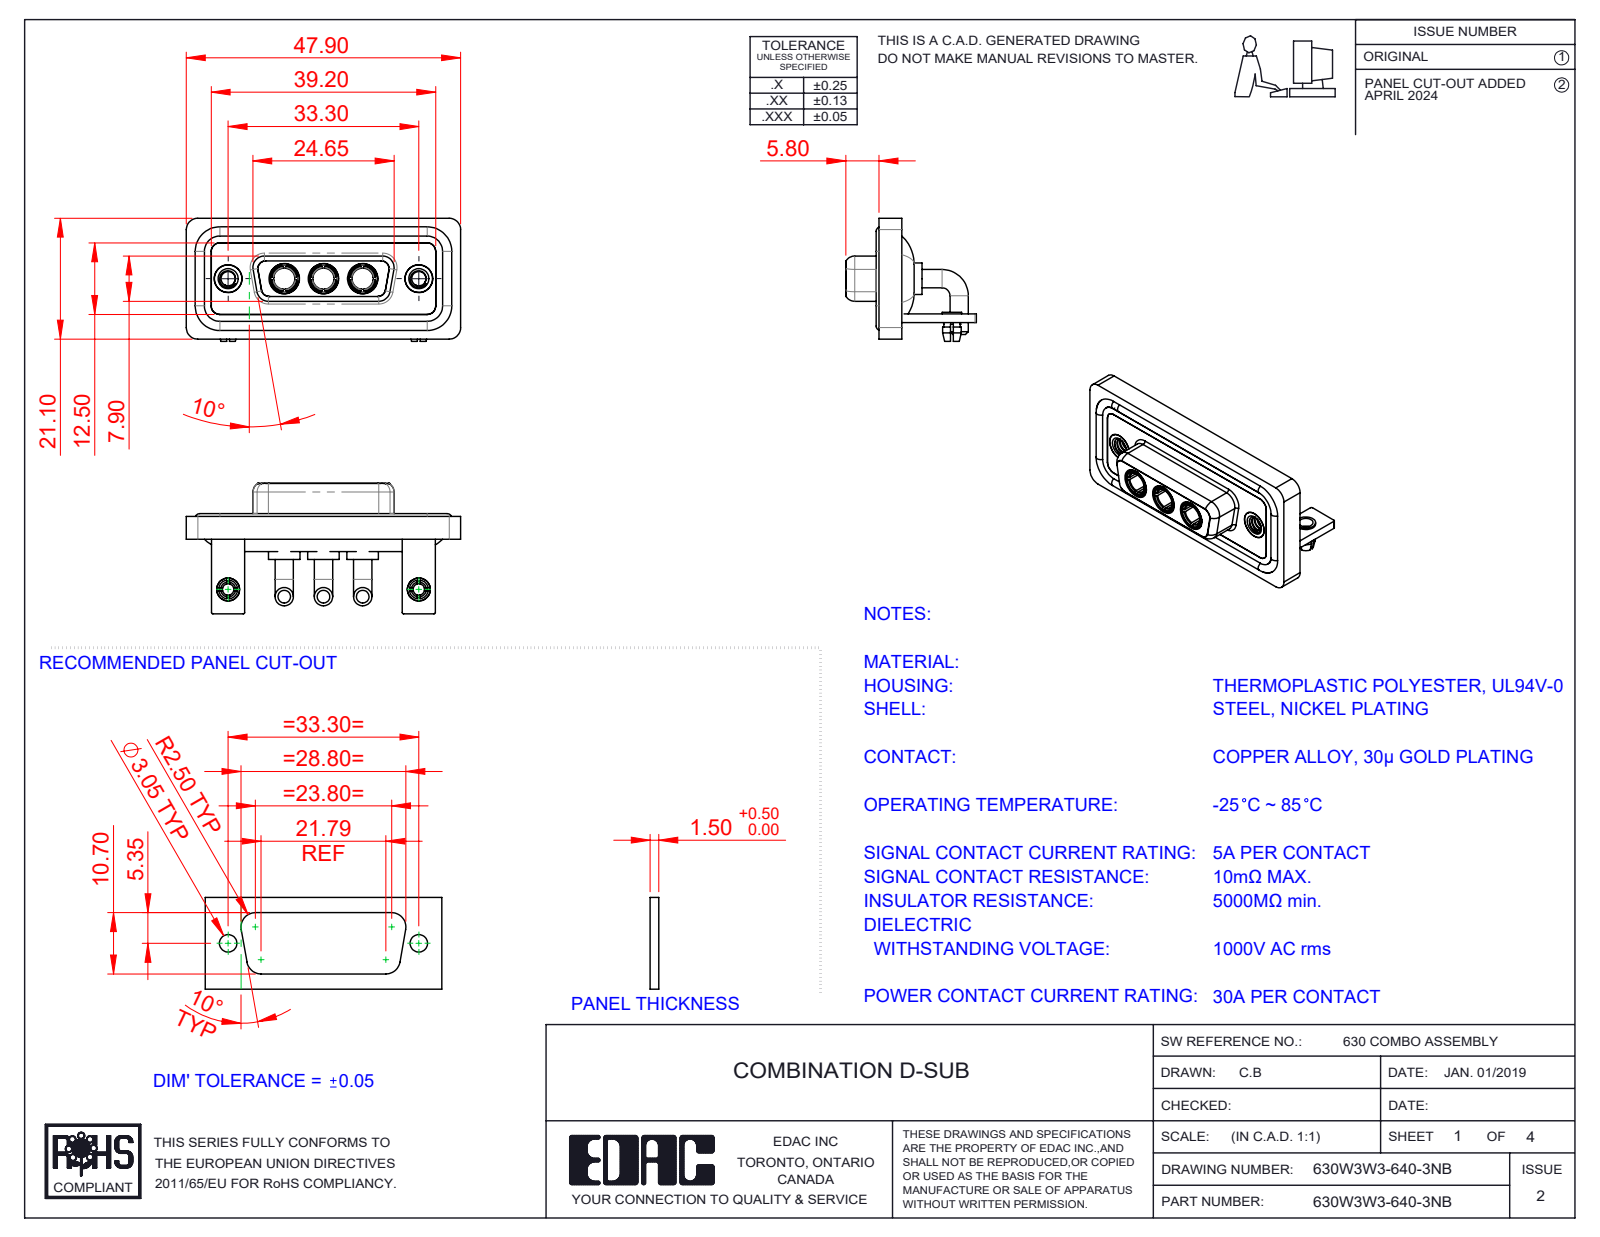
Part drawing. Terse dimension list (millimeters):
name: 630W3W3-640-3NB; 630Combo Shell Front_15 Contacts; 630Combo Housing_3W3; 630Combo Stabilizer Bracket_50 Contacts (+5 more)
written by: SolidWorks 2023 (CONFIG_CONTROL_DESIGN)
unit: mm
bodies: 17 solids, 754 faces (260 planar, 317 cylindrical, 177 other)
size: 47.9 × 22.8 × 21.5
volume: 6 659 mm³; area: 10 976 mm²
holes: 5× ⌀4.85, 4× ⌀2.5, 3× ⌀3.7, 3× ⌀5.3, 2× ⌀2, 2× ⌀3.2, 2× ⌀4, 2× ⌀4.05, 2× ⌀5
bosses: 6× ⌀3.2, 4× ⌀1.6, 3× ⌀5.5, 3× ⌀5.2, 3× ⌀4.96, 3× ⌀4.75, 3× ⌀3.75, 2× ⌀4.95
rounds: 21× R2, 18× R1.5, 16× R0.25, 12× R1.35, 8× R1.6, 5× R0.5, 4× R0.6, 4× R0.65
face distances: 0.4, 2.9, 1.5, 1.8, 3.7, 1.1, 4.1, 1.6, 2.5, 1.4
hole spacings: 6.85, 9.8, 16.65, 23.5, 33.3, 13.7
